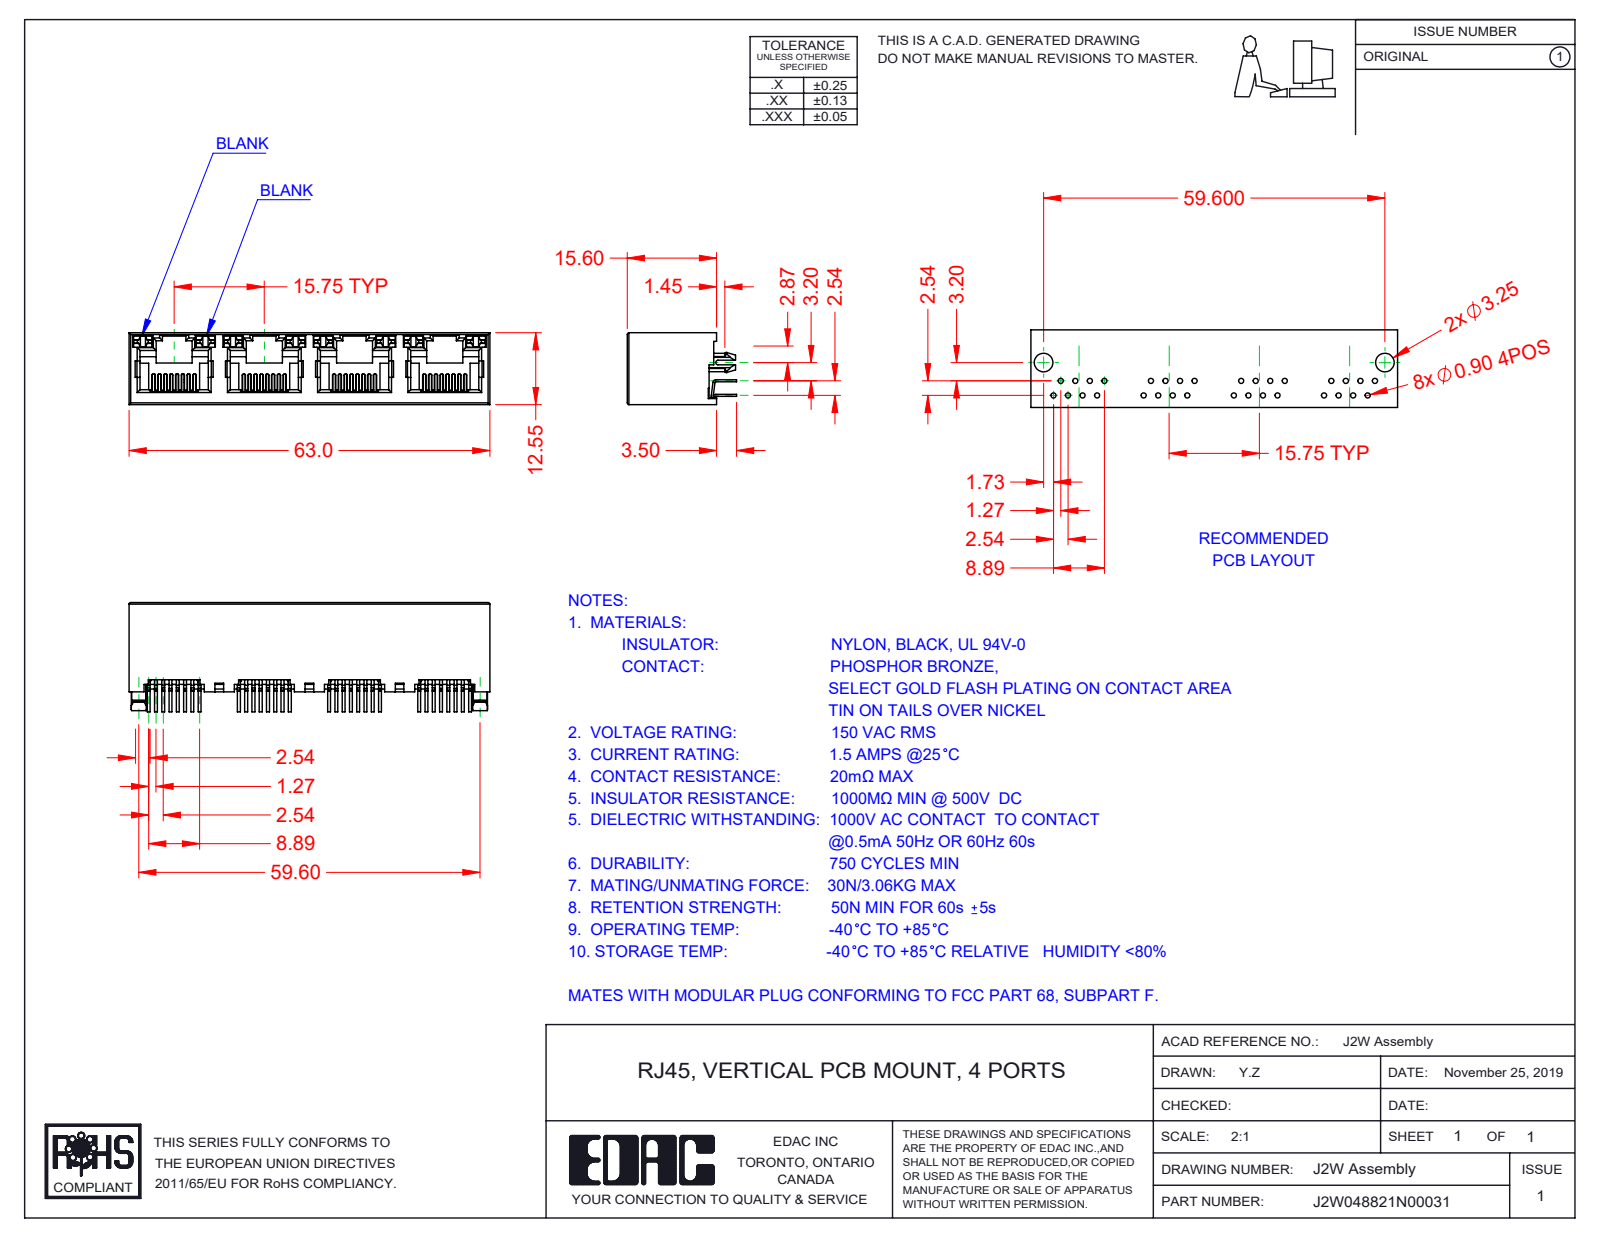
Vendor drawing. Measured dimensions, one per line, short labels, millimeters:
name: 2W LED RH_0-Blank; 2W Insulator; J2W048821N00031; 2W Contacts (+2 more)
written by: SolidWorks 2020 (CONFIG_CONTROL_DESIGN)
unit: mm
bodies: 37 solids, 2879 faces (2416 planar, 405 cylindrical, 58 other)
size: 63 × 19.09 × 12.55
volume: 5 090 mm³; area: 12 247 mm²
rounds: 64× R0.15, 29× R0.2, 28× R0.5, 13× R0.3, 8× R0.45, 2× R1.5, 2× R1.6, 2× R1.75
face distances: 12.55, 11.9, 0.65, 15.75, 0.36, 1.5, 0.6, 0.78, 11.3, 31.5
